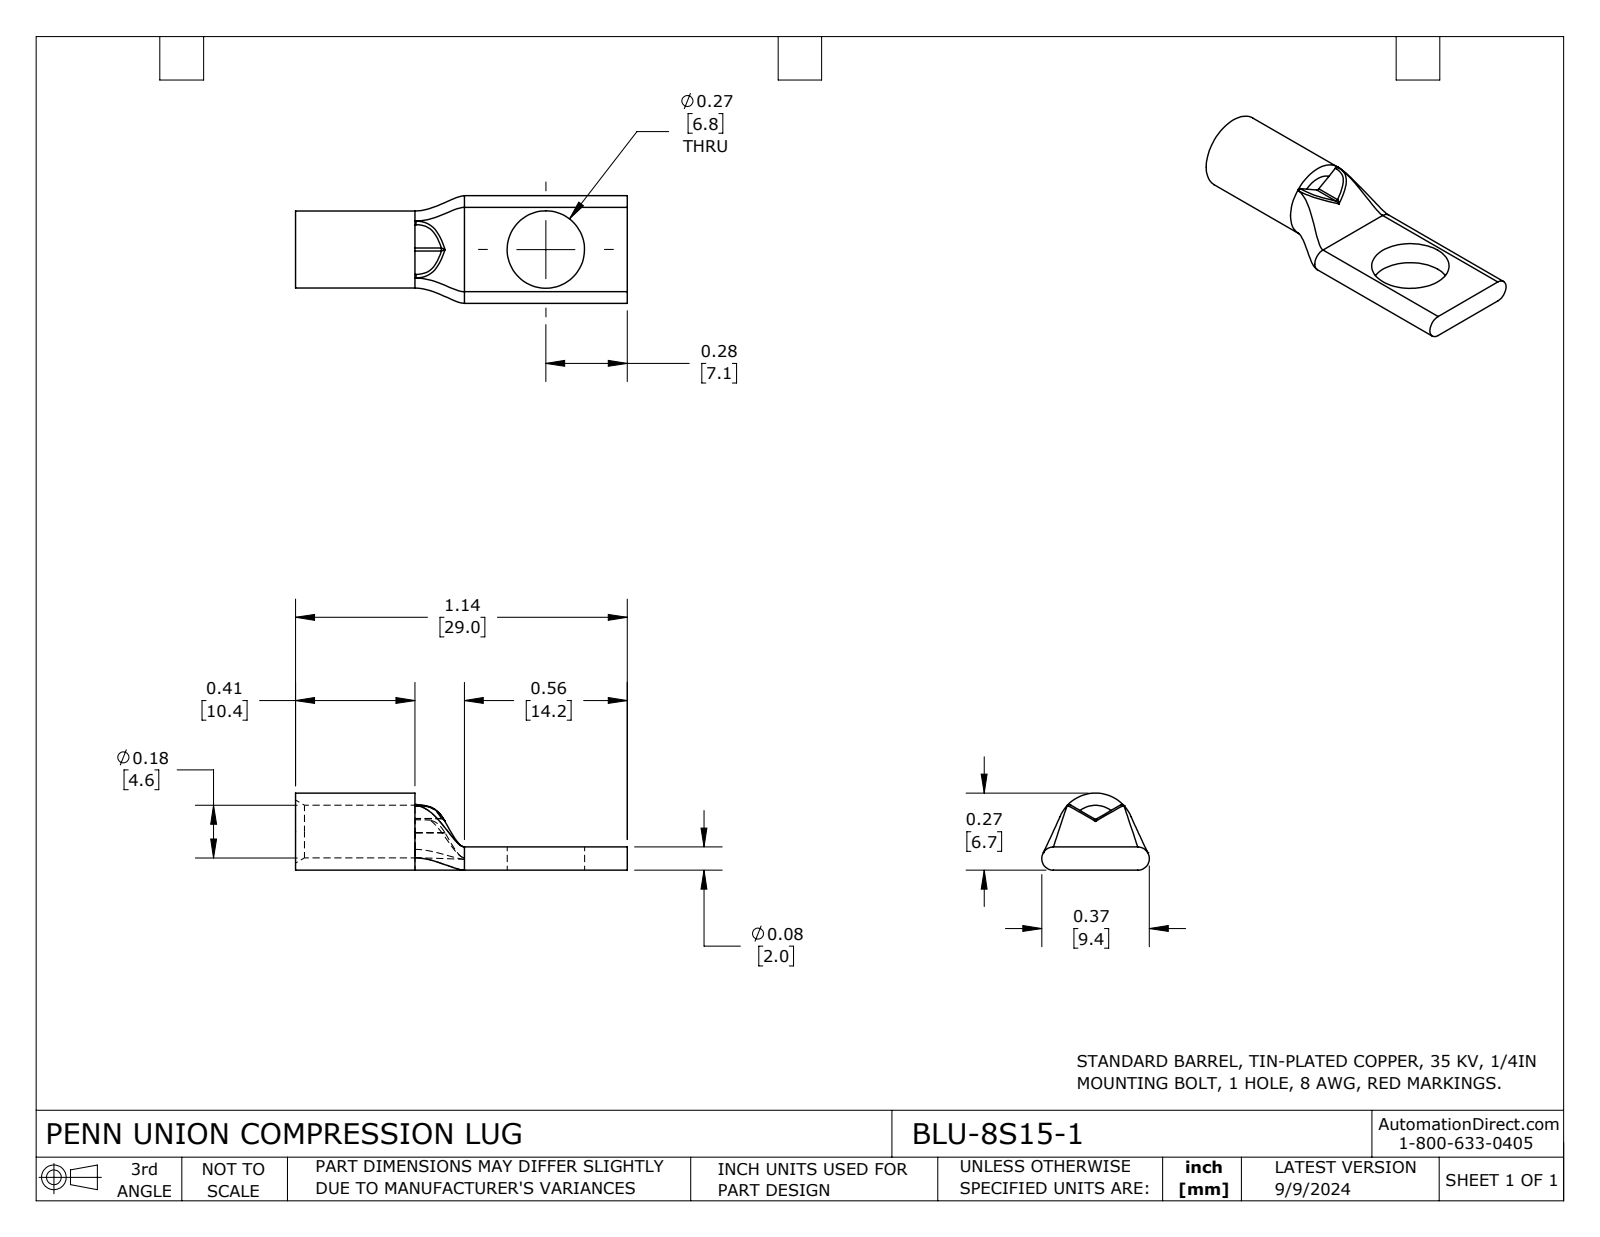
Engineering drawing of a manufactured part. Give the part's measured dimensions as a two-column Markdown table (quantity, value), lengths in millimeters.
| quantity | value |
| --- | --- |
| part name | BLU-8S15-1 |
| STEP written by | SolidWorks 2023 (CONFIG_CONTROL_DESIGN) |
| units | millimeters |
| bodies | 1 solid, 37 faces (11 planar, 11 cylindrical, 15 other) |
| overall size | 29 × 9.4 × 6.7 |
| volume | 460 mm³ |
| surface area | 861 mm² |
| round holes (diameter × count) | 4.6 × 1, 6.8 × 1 |
| round bosses / shafts (diameter × count) | 6.7 × 1 |
| partial cylindrical surfaces (radius × count) | 0.3 × 2, 1 × 2 |
| main face-to-face distances | 2, 29, 10.4, 18.5, 1.1, 14.7, 4.3, 14.2 |
